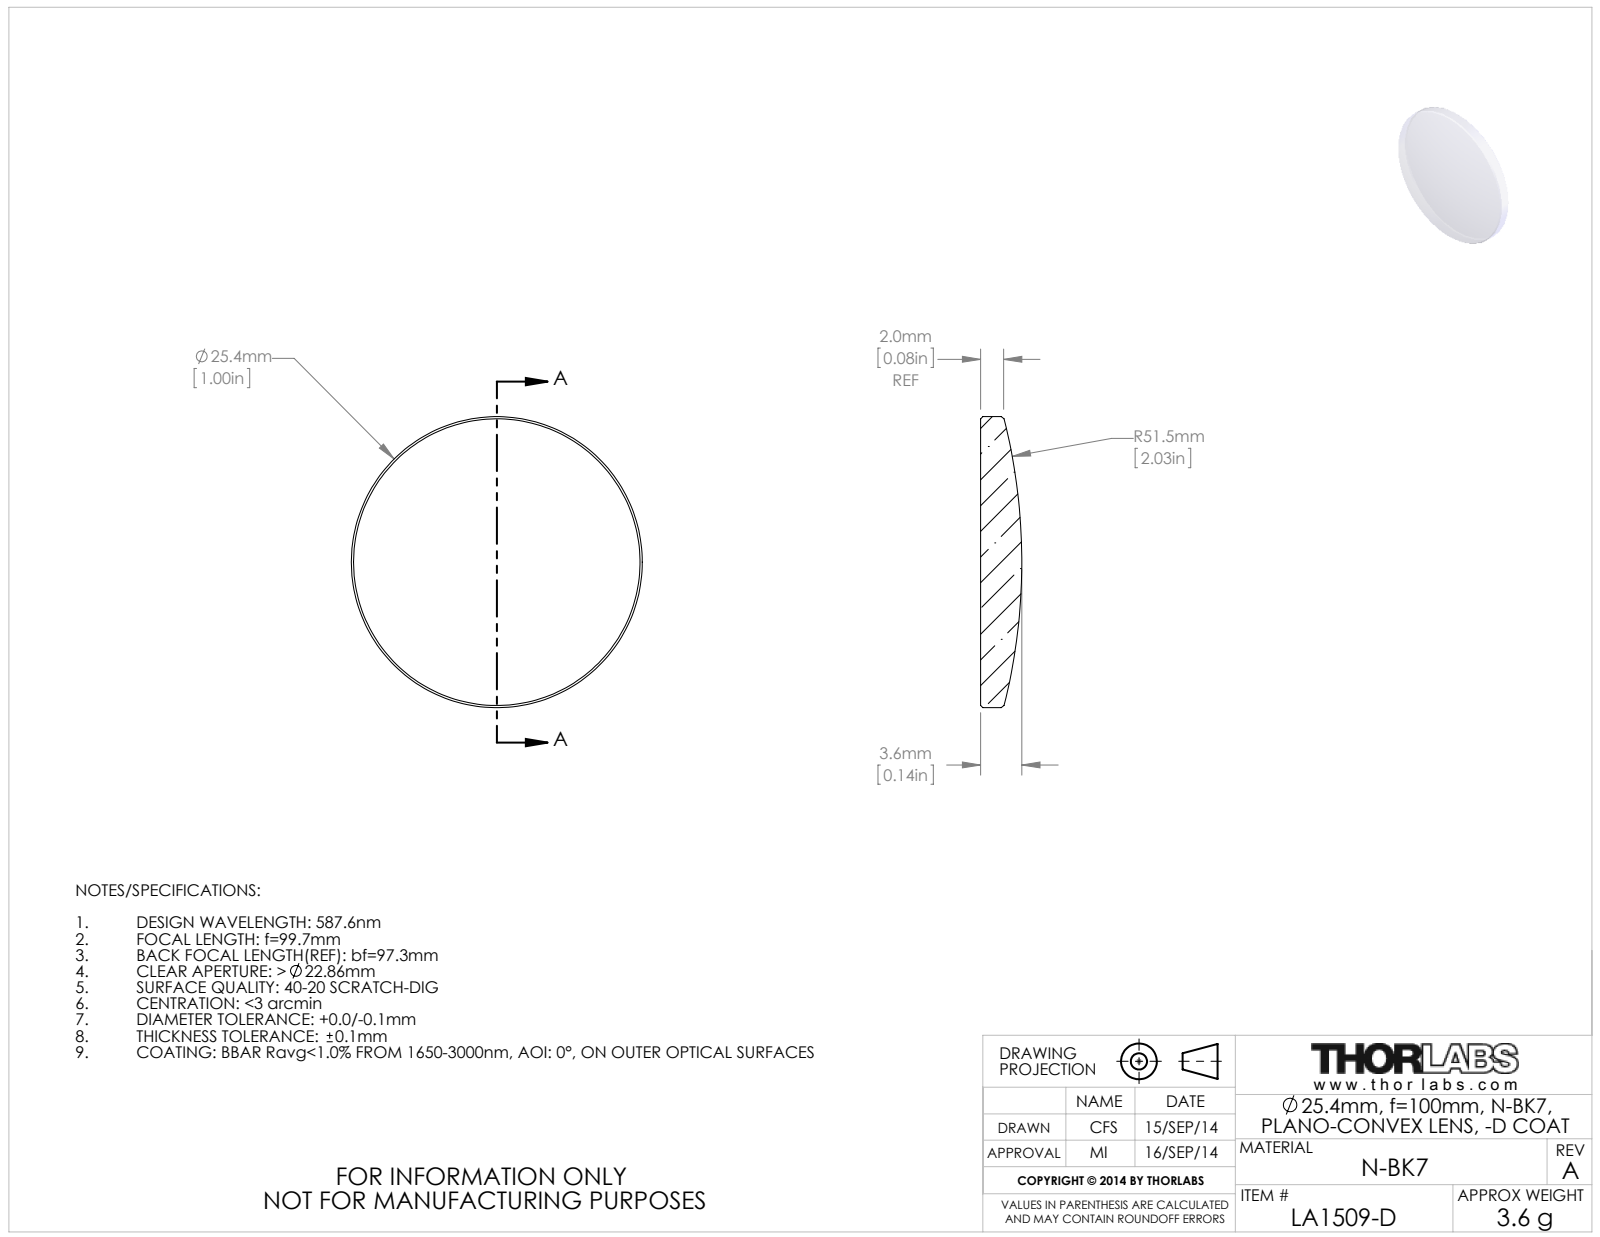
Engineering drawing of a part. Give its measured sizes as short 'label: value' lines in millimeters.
name: TTN031785-E0W
written by: SolidWorks 2014 (CONFIG_CONTROL_DESIGN)
unit: mm
bodies: 1 solid, 9 faces (1 planar, 2 cylindrical, 6 other)
size: 25.4 × 25.4 × 3.6
volume: 1 400 mm³; area: 1 166 mm²
bosses: 1× ⌀25.4
